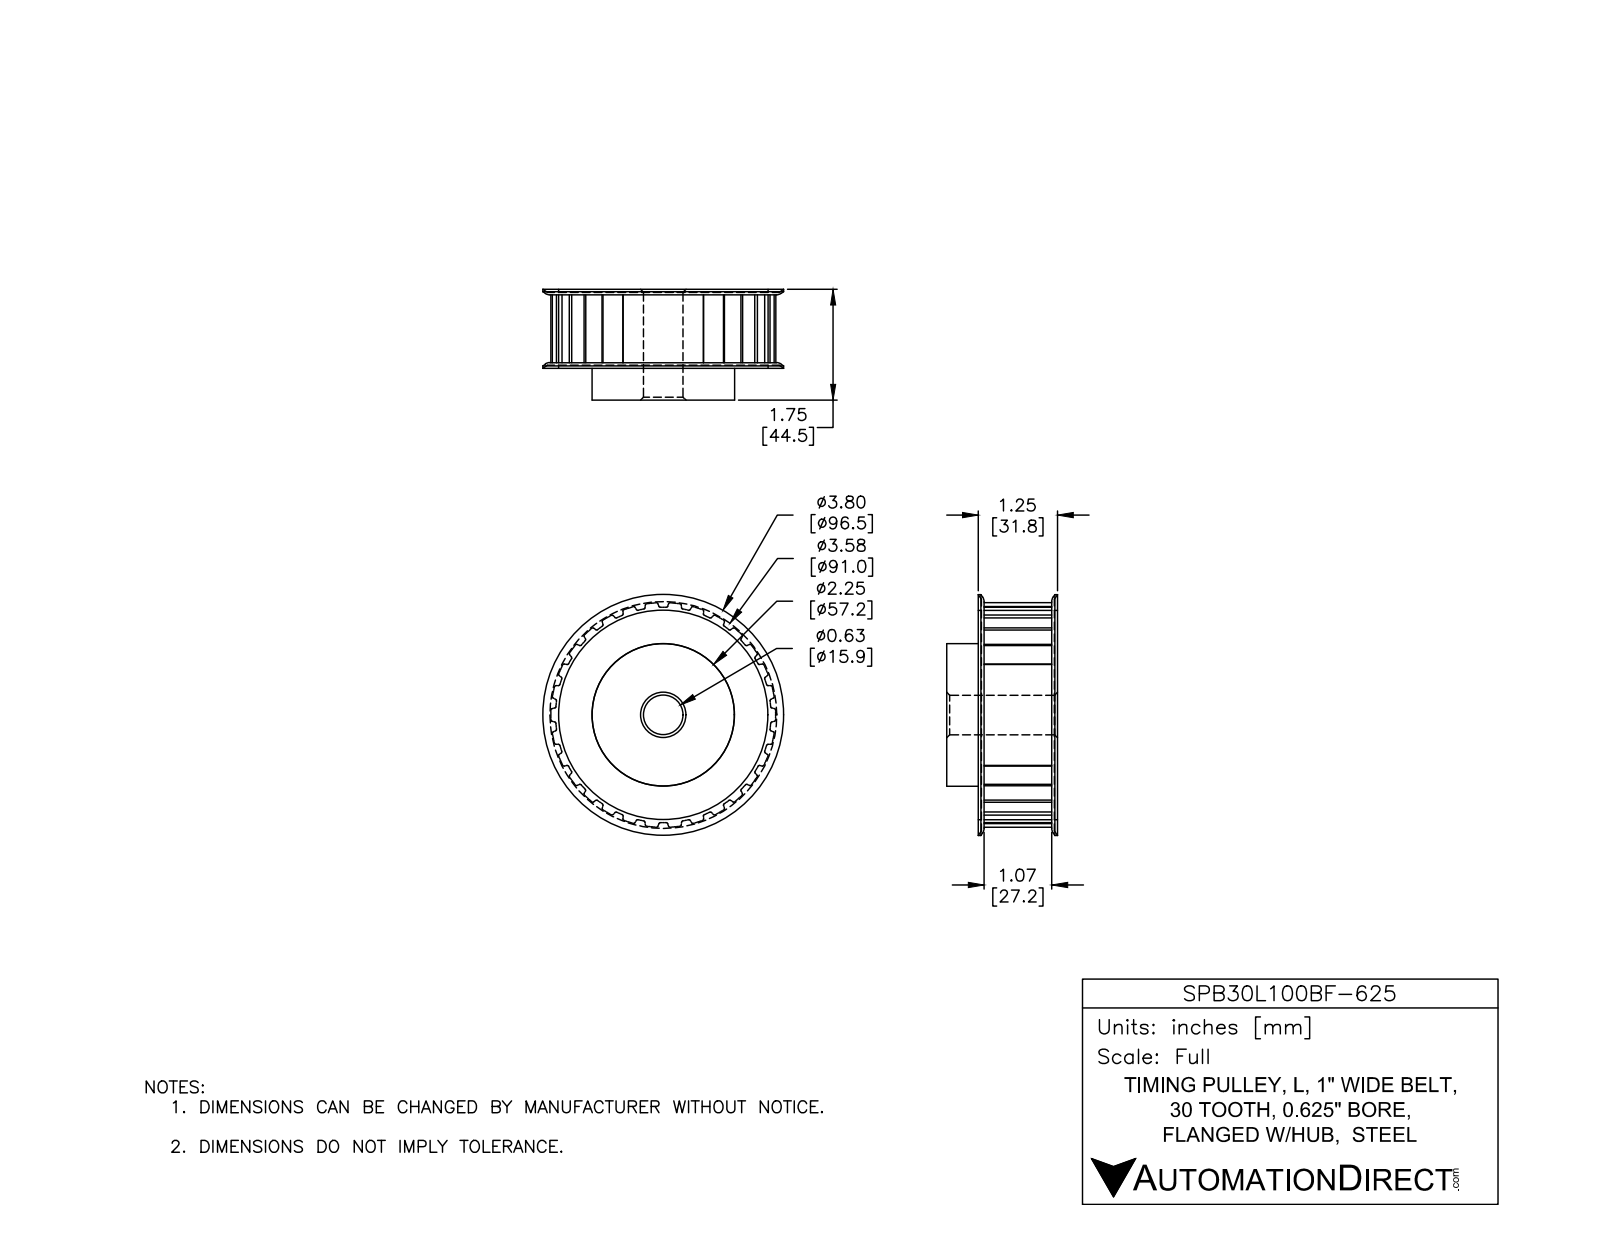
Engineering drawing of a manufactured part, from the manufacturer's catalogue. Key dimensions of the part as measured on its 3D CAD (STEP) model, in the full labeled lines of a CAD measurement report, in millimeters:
Part name (STEP PRODUCT): SPB30L100BF-625
STEP written by: SolidWorks 2019 (CONFIG_CONTROL_DESIGN)
Units: millimetres
Bodies: 1 solid, 304 faces (97 planar, 187 cylindrical, 20 other)
Overall size (bounding box): 96.5 × 96.5 × 44.5
Volume: 238 400 mm³ · Surface area: 32 530 mm²
Round holes (diameter × count): ⌀15.9 ×1
Round bosses / shafts (diameter × count): ⌀96.5 ×1, ⌀84 ×1, ⌀71.4 ×1
Partial cylindrical surfaces — rounded edges, fillets, slot ends (radius × count): R0.5 ×120, R45.1 ×1
Main face-to-face distances: 44.5, 1.3, 30.5, 31.8, 12.7, 14, 29.2, 43.2, 2.3, 29.5
